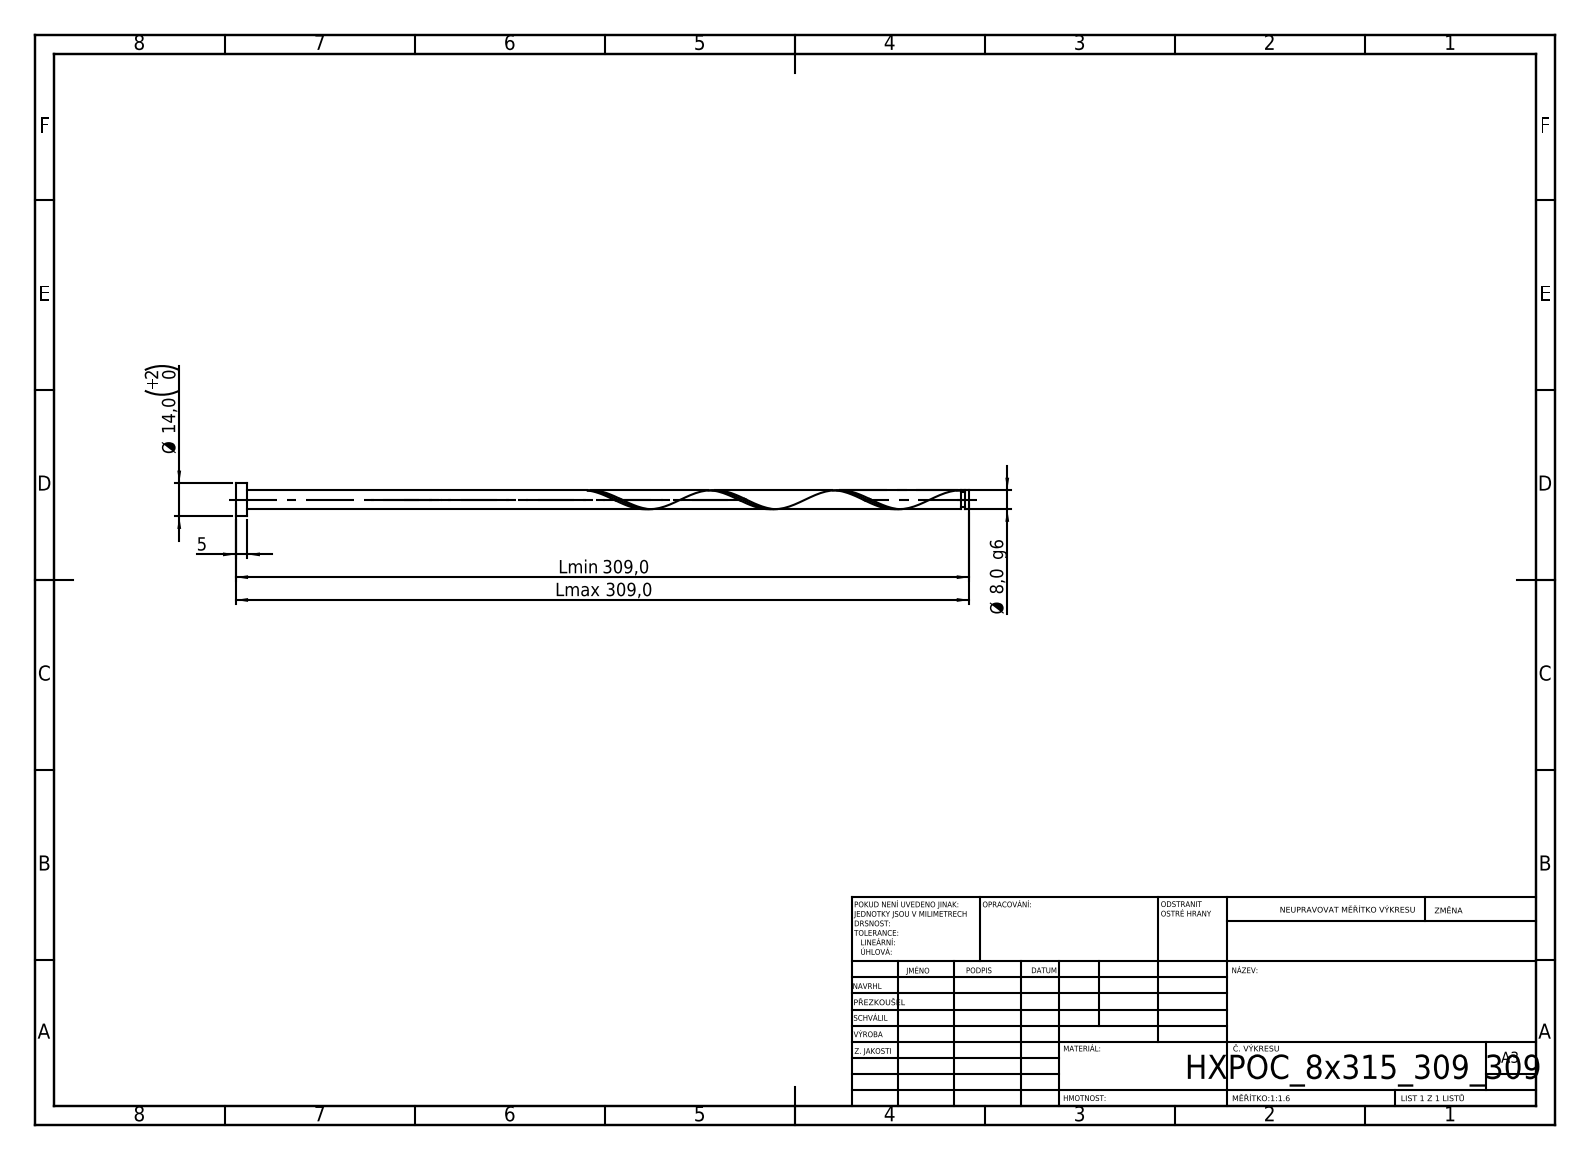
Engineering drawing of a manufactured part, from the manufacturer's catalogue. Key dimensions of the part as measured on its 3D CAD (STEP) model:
STEP written by: SolidWorks 2019 (CONFIG_CONTROL_DESIGN)
Units: millimetres
Bodies: 1 solid, 21 faces (6 planar, 14 cylindrical, 1 other)
Overall size (bounding box): 309 × 14 × 14
Volume: 15 870 mm³ · Surface area: 8 334 mm²
Round bosses / shafts (diameter × count): ⌀14 ×1, ⌀8 ×1, ⌀6.4 ×1
Main face-to-face distances: 5, 309, 304, 307.05, 302.05, 1.95, 305.45, 300.45, 1.6, 3.55
